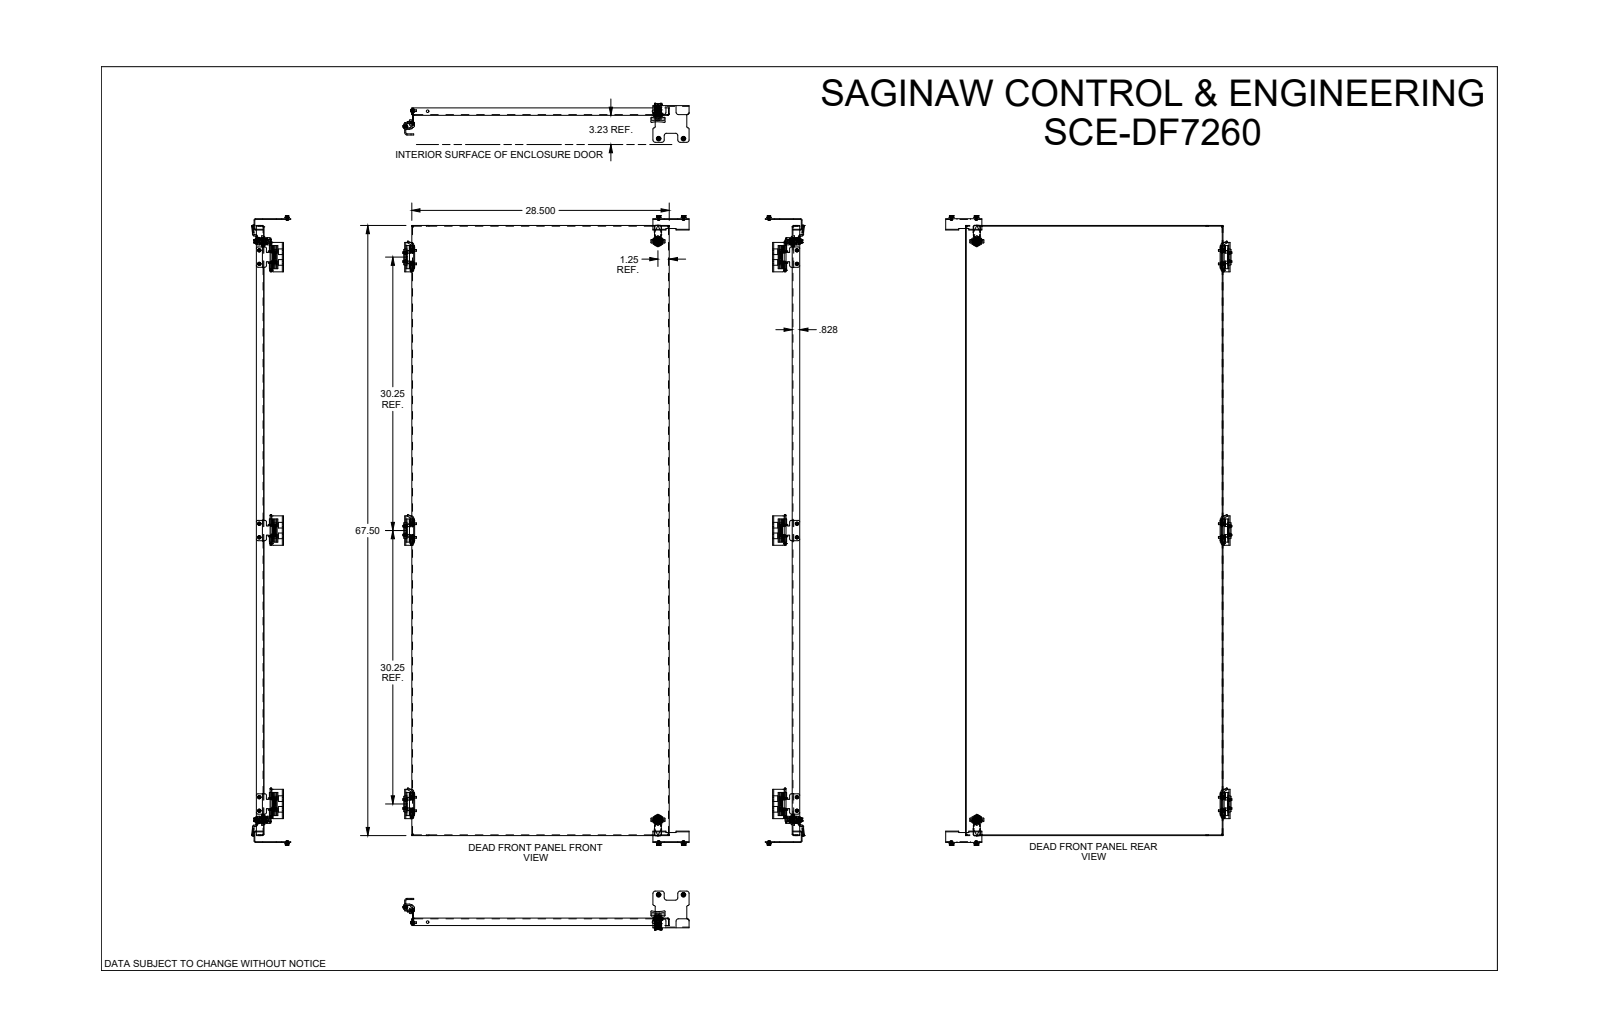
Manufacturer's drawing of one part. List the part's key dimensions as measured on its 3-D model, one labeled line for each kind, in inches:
Part name (STEP PRODUCT): SCE-DF7260
STEP written by: SolidWorks 2021 (AUTOMOTIVE_DESIGN)
Units: inches
Bodies: 56 solids, 2317 faces (1122 planar, 676 cylindrical, 519 other)
Overall size (bounding box): 69.688 × 31.679 × 4.32
Volume: 136 in³ · Surface area: 4 402 in²
Round holes (diameter × count): ⌀0.19 ×8, ⌀0.172 ×6, ⌀0.21 ×6, ⌀0.244 ×6, ⌀0.25 ×6, ⌀0.266 ×6, ⌀0.197 ×2, ⌀0.315 ×2, ⌀0.394 ×2, ⌀0.433 ×2, ⌀0.634 ×2, ⌀0.222 ×1
Round bosses / shafts (diameter × count): ⌀0.17 ×8, ⌀0.373 ×6, ⌀0.34 ×6, ⌀0.25 ×6, ⌀0.249 ×6, ⌀0.188 ×6, ⌀0.196 ×4, ⌀1.102 ×2
Partial cylindrical surfaces — rounded edges, fillets, slot ends (radius × count): R0.012 ×56, R0.25 ×23, R0.02 ×22, R0.157 ×16, R0.062 ×14, R0.01 ×13, R0.068 ×9, R0.125 ×9
Main face-to-face distances: 0.06, 28.44, 28.5, 28.38, 0.078, 67.44, 0.672, 0.732, 68.112, 68.172
Hole centre spacings: 30.25, 0.985, 1.749, 1.75, 2.13, 2.13, 60.5, 29.059
